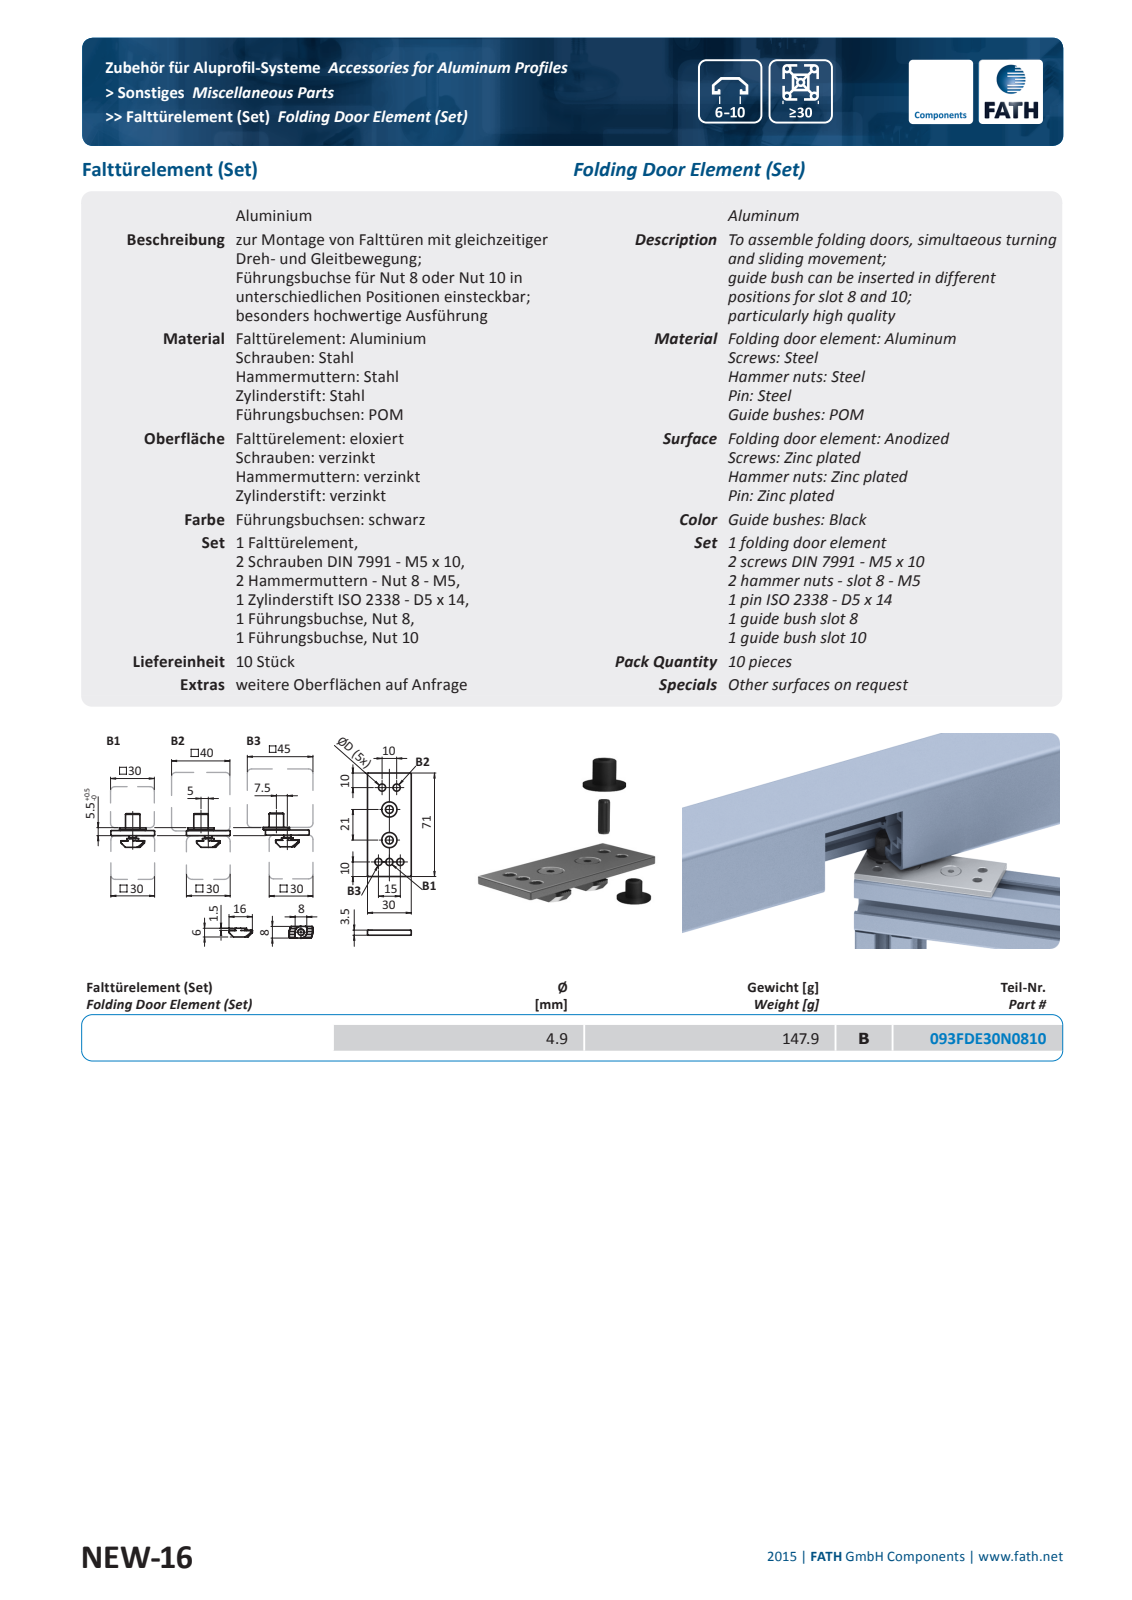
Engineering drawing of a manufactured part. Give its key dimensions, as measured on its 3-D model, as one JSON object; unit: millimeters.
{"part_name": "fath_093fde30n0810_1; fath_093fde30n0810_2; fath_093fde30n0810_3; fath_093fde30n0810_4 (+4 more)", "step_written_by": "Spatial InterOp 3D (automotive_design)", "units": "millimeters", "bodies": {"solids": 8, "faces": 430, "planar": 134, "cylindrical": 172, "other": 124}, "overall_size": [71, 50, 23.1], "volume_mm3": 9978, "surface_area_mm2": 8710, "round_holes": [[4.9, 5], [4.1, 2], [5, 2], [5.3, 2], [6.2, 2]], "round_bosses_or_shafts": [[9.64, 2], [5, 2], [18, 1], [16, 1], [9.9, 1], [7.9, 1]], "partial_cylinders_radius": [[0.5, 20], [0.1, 14], [1, 4], [4, 2], [8, 2]], "face_to_face_distances": [3.5, 5.3, 1.8, 8, 21, 2, 29, 30, 3.3, 11.3], "hole_center_spacings": [7.5, 15, 15.81, 16.77, 36.35, 36.77, 51.06, 51.24]}
